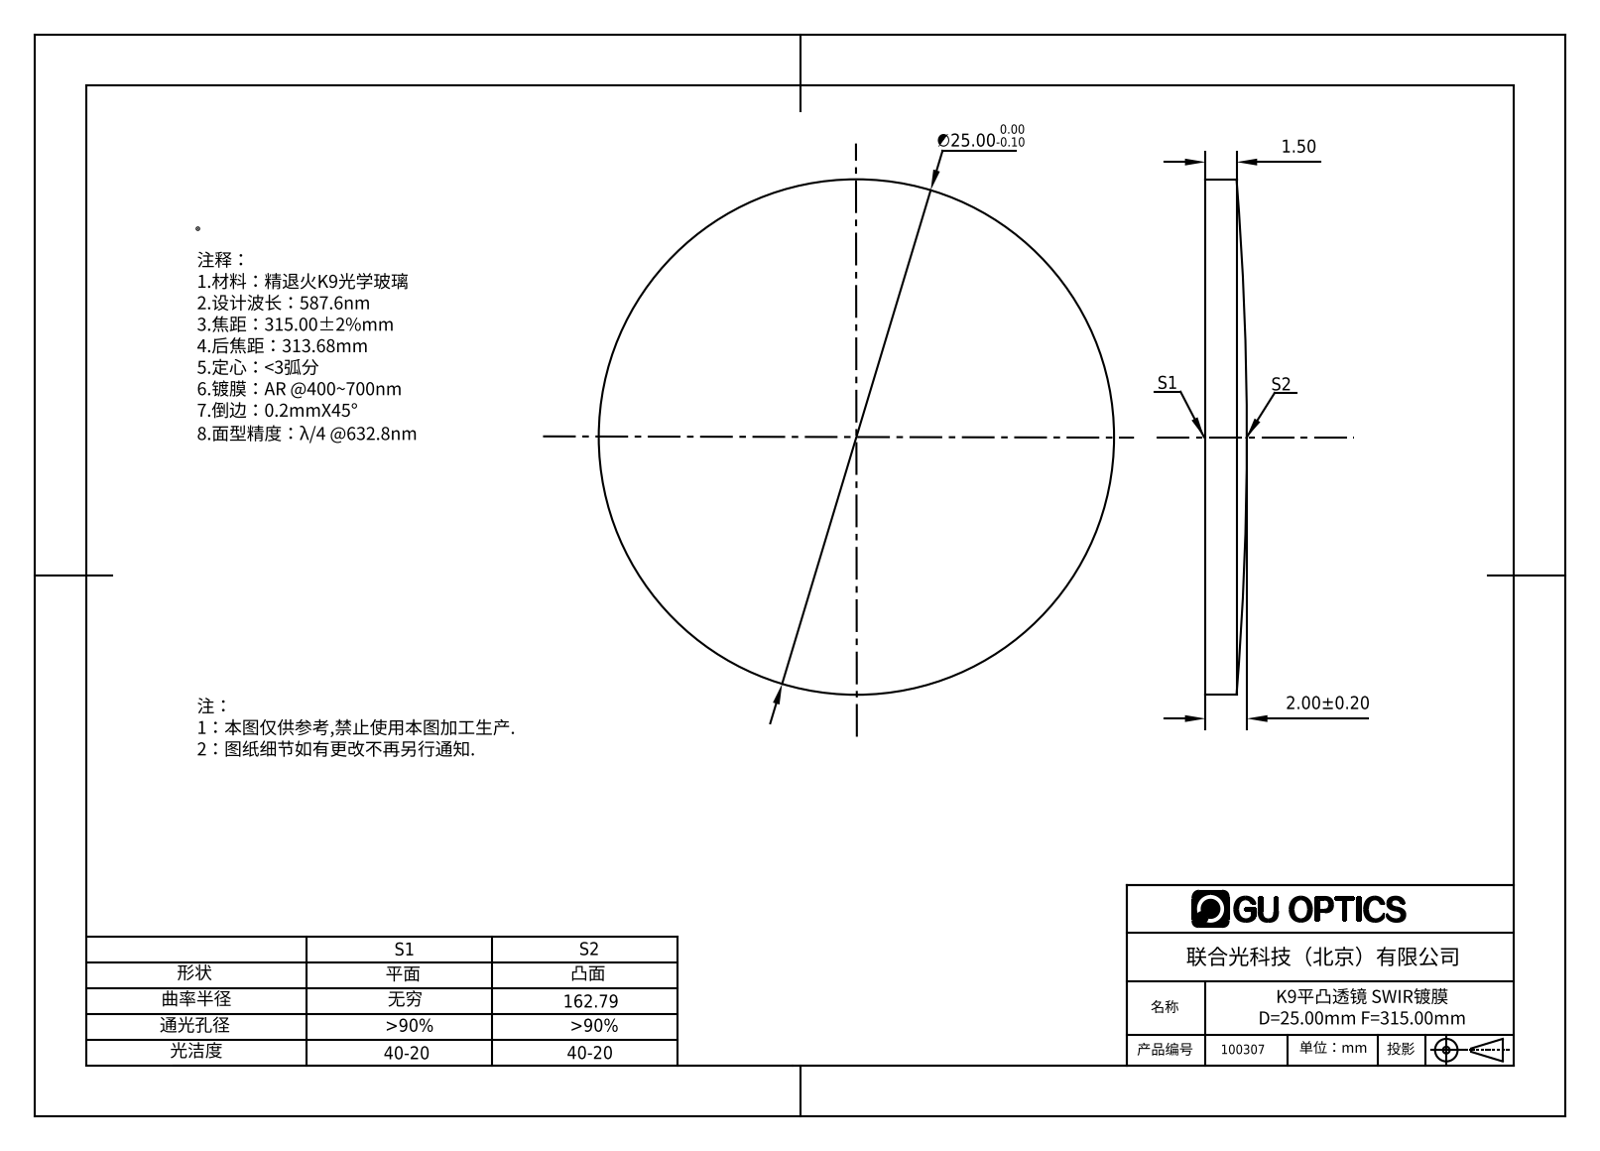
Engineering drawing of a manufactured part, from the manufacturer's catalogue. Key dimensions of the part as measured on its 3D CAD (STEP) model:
Part name (STEP PRODUCT): 100135
STEP written by: SolidWorks 2016 (AUTOMOTIVE_DESIGN)
Units: millimetres
Bodies: 1 solid, 5 faces (1 planar, 2 cylindrical, 2 other)
Overall size (bounding box): 25 × 25 × 2
Volume: 859 mm³ · Surface area: 1 100 mm²
Round bosses / shafts (diameter × count): ⌀25 ×1
